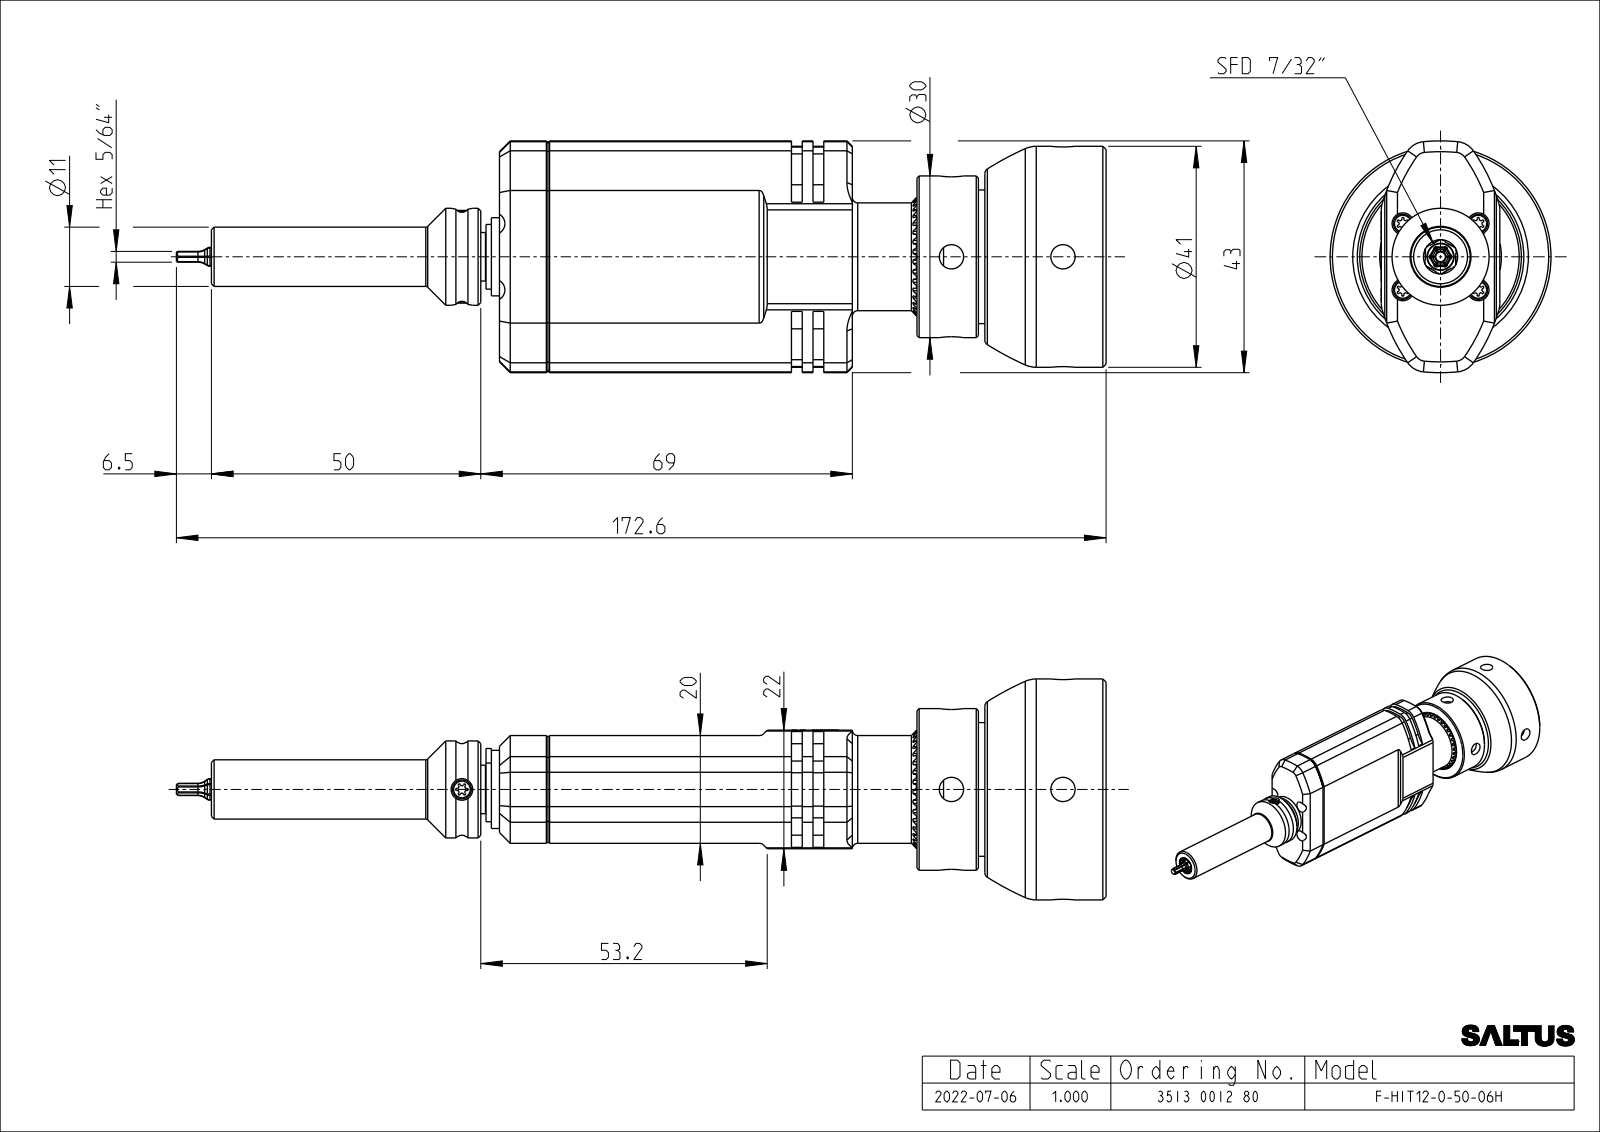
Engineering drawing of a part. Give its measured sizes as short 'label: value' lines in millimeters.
name: EXT_COMP_SW0010
written by: CREO PARAMETRIC BY PTC INC, 2020281 (CONFIG_CONTROL_DESIGN)
unit: mm
bodies: 1 solid, 1130 faces (582 planar, 340 cylindrical, 208 other)
size: 172.6 × 43 × 41
volume: 96 410 mm³; area: 19 720 mm²
holes: 5× ⌀4, 4× ⌀4.5, 2× ⌀1.2, 1× ⌀8.6, 1× ⌀9.1, 1× ⌀22, 1× ⌀26.5
bosses: 5× ⌀3.5, 1× ⌀41, 1× ⌀30, 1× ⌀26, 1× ⌀26, 1× ⌀24.8, 1× ⌀20.2, 1× ⌀20
rounds: 42× R0.2, 30× R0.3, 18× R1, 12× R2.5, 8× R4, 6× R33, 6× R34, 4× R3
face distances: 20, 1, 21, 47.1, 112.6, 65.5, 35.1, 12, 77.5, 22.5
hole spacings: 9.3, 4.5, 6.2, 8.1, 12.3, 13.6, 14, 15.2
